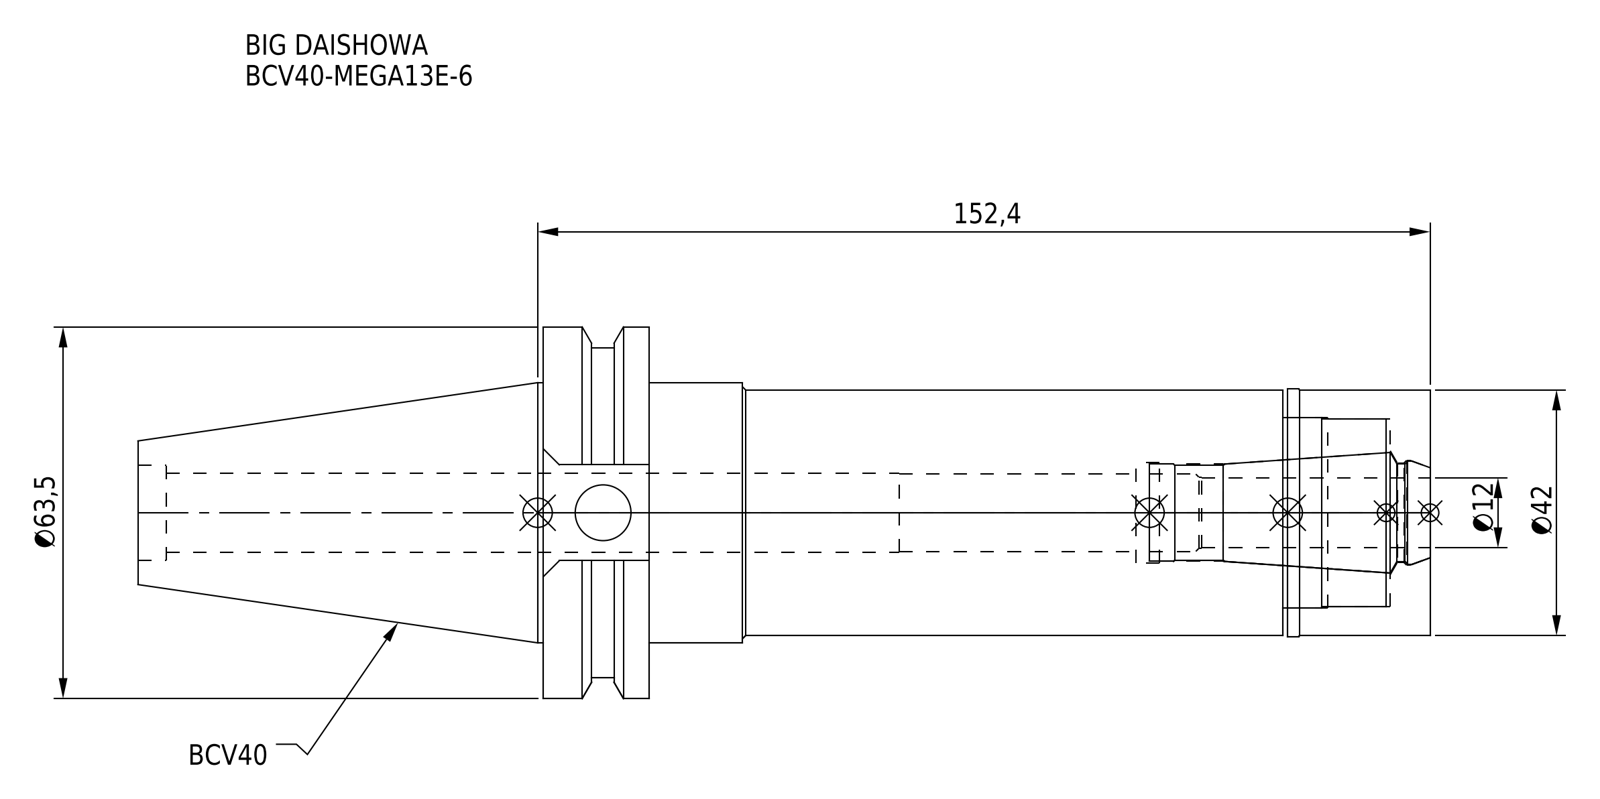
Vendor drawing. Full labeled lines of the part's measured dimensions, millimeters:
Part name (STEP PRODUCT): DXF_TEMP_ASSY_ASM_4_ASM.stp; BCV40-MEGA13E-6-120.stp; BCV40-MEGA13E-6-120-FreeParts; MEN13_1.stp (+3 more)
STEP written by: SolidWorks 2019 (CONFIG_CONTROL_DESIGN)
Units: millimetres
Bodies: 2 solids, 90 faces (30 planar, 42 cylindrical, 18 other)
Overall size (bounding box): 220.65 × 63.5 × 61.35
Volume: 265 977 mm³ · Surface area: 50 159 mm²
Round holes (diameter × count): ⌀9.53 ×1, ⌀13.3 ×1, ⌀13.6 ×1, ⌀16.32 ×1, ⌀16.6 ×1, ⌀17 ×1, ⌀17.2 ×1, ⌀17.9 ×1, ⌀32 ×1, ⌀32.5 ×1
Round bosses / shafts (diameter × count): ⌀63.5 ×1, ⌀56.36 ×1, ⌀44.45 ×1, ⌀42.3 ×1, ⌀42 ×1
Main face-to-face distances: 18.05, 133.35, 151.4, 25.1, 24.3, 109.05, 127.1, 0.8, 108.25, 126.3
